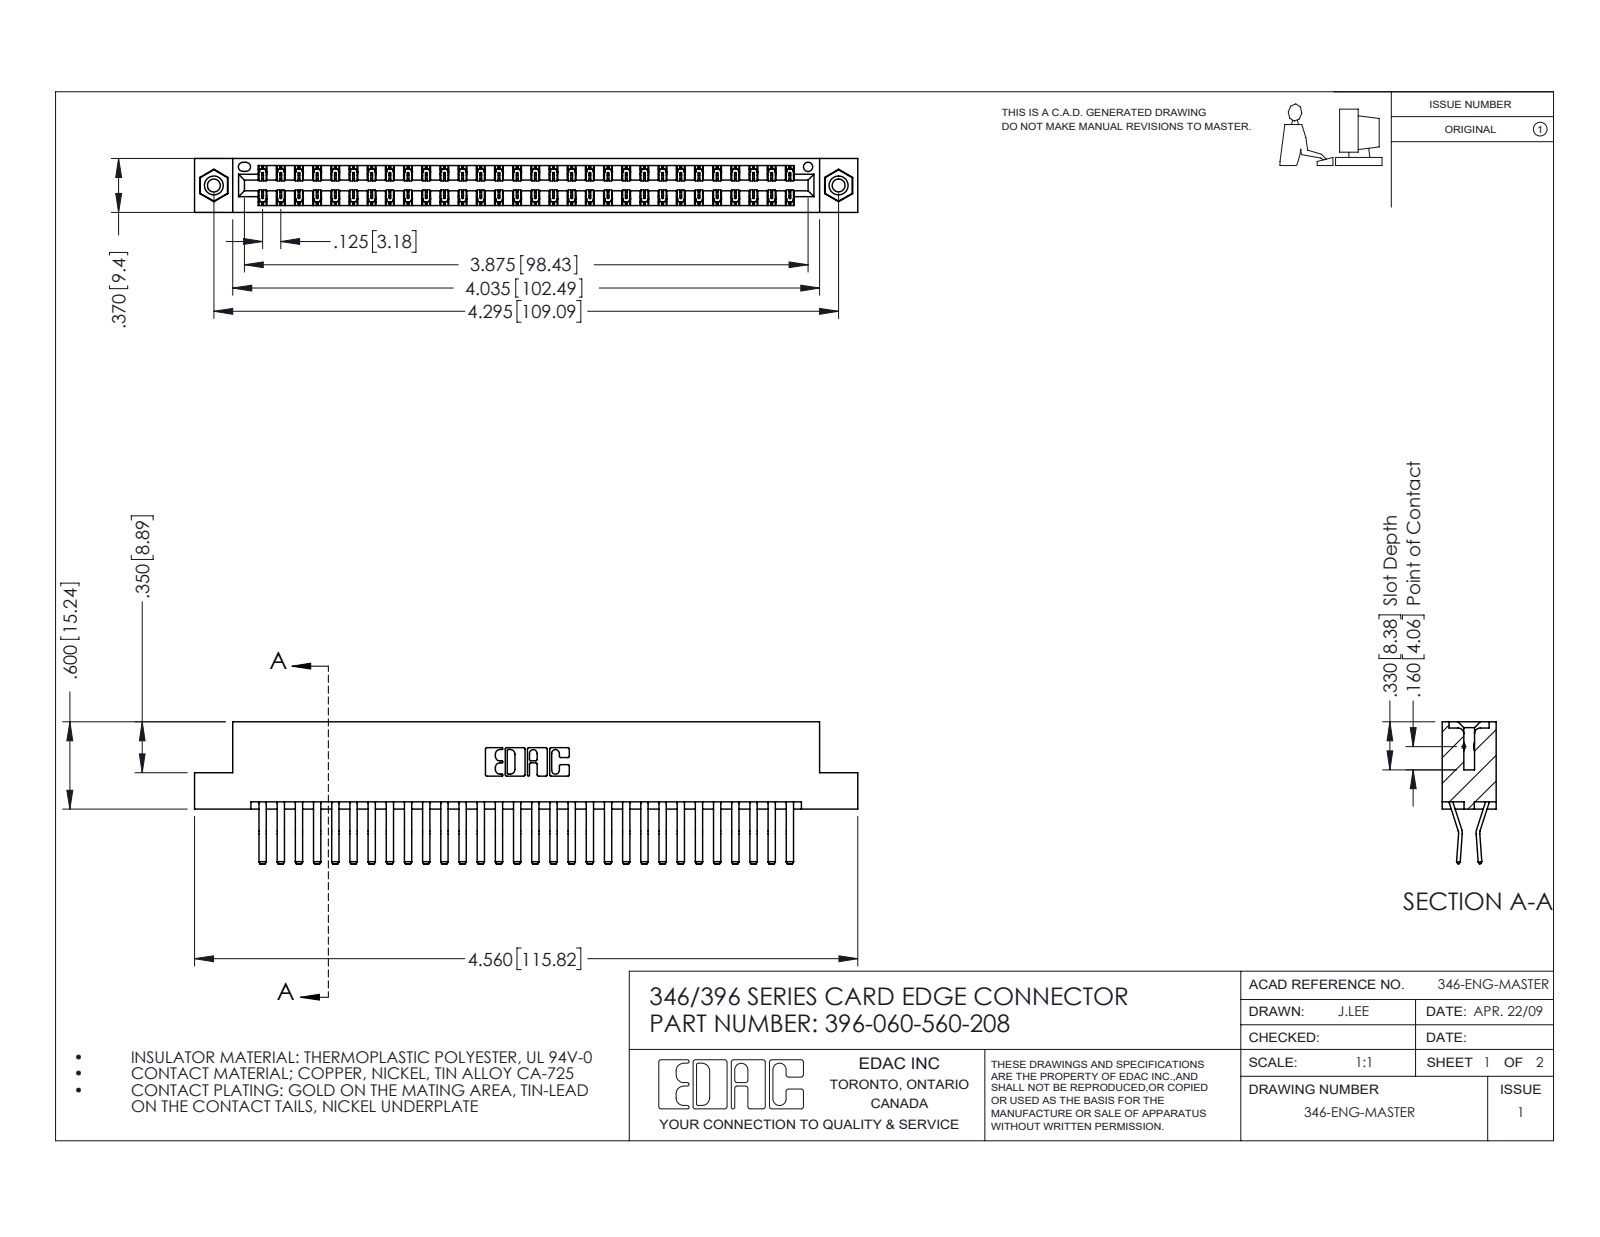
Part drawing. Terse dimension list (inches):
name: 346 Part_Flush Mounting Lugs - 0.156 Dia-TI; 345-292-001_560 Tail; 396-060-560-208; 345-250-001_345-250-003-102
written by: SolidWorks 2016 (CONFIG_CONTROL_DESIGN)
unit: in
bodies: 63 solids, 3422 faces (2208 planar, 1198 cylindrical, 16 other)
size: 4.56 × 0.975 × 0.37
volume: 0.707 in³; area: 26.05 in²
holes: 2× ⌀0.089, 2× ⌀0.125, 2× ⌀0.156, 1× ⌀0.064
bosses: 2× ⌀0.155
rounds: 90× R0.006, 22× R0.01, 6× R0.007, 6× R0.031, 3× R0.026, 2× R0.01, 2× R0.014, 2× R0.022
face distances: 0.048, 0.322, 0.37, 0.25, 0.025, 0.072, 0.298, 0.275, 0.148, 0.222
hole spacings: 0.246, 4.087, 4.295
